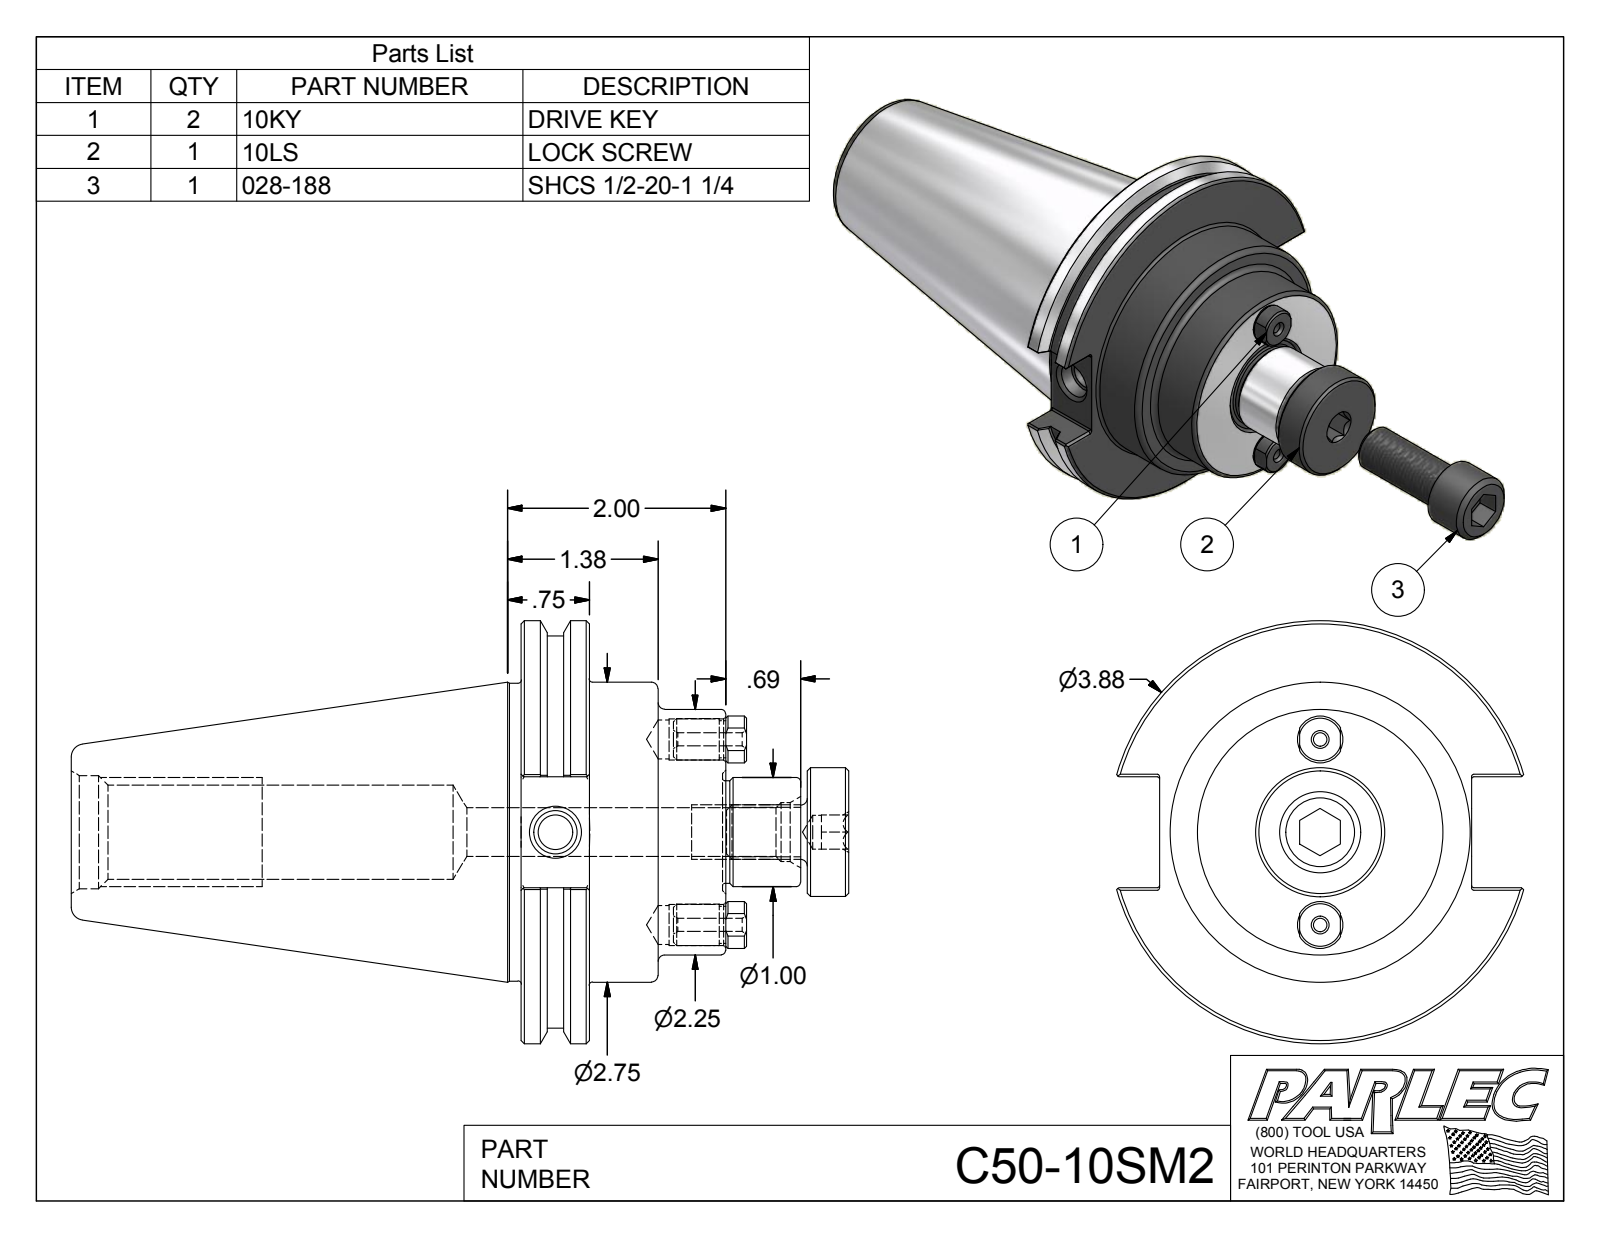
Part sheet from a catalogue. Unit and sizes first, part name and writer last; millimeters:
Units: millimetres
Overall size (bounding box): 238.2 × 98.4 × 94.7
Round holes (diameter × count): ⌀3 ×2, ⌀9 ×2, ⌀9.5 ×2, ⌀7.9 ×1, ⌀8 ×1, ⌀10.1 ×1, ⌀11.3 ×1, ⌀13.7 ×1, ⌀22 ×1, ⌀26.4 ×1
Round bosses / shafts (diameter × count): ⌀9.7 ×2, ⌀8.6 ×2, ⌀98.4 ×1, ⌀91.3 ×1, ⌀69.9 ×1, ⌀69.3 ×1, ⌀57.2 ×1, ⌀30 ×1
Partial cylindrical surfaces — rounded edges, fillets, slot ends (radius × count): R0.5 ×12, R5.4 ×2
Main face-to-face distances: 15.9, 31.8, 47.6, 31.9, 16, 15.7, 76.3, 60.4, 44.4, 28.6
Hole centre spacings: 21.6, 43.2
Volume: 446 400 mm³ · Surface area: 60 950 mm²
Bodies: 5 solids, 177 faces (68 planar, 48 cylindrical, 61 other)
Part name (STEP PRODUCT): C50-10SM2; C50-10SM2-1; 028-188; 10KY (+1 more)
STEP written by: Autodesk Inventor 2012 (AUTOMOTIVE_DESIGN)
